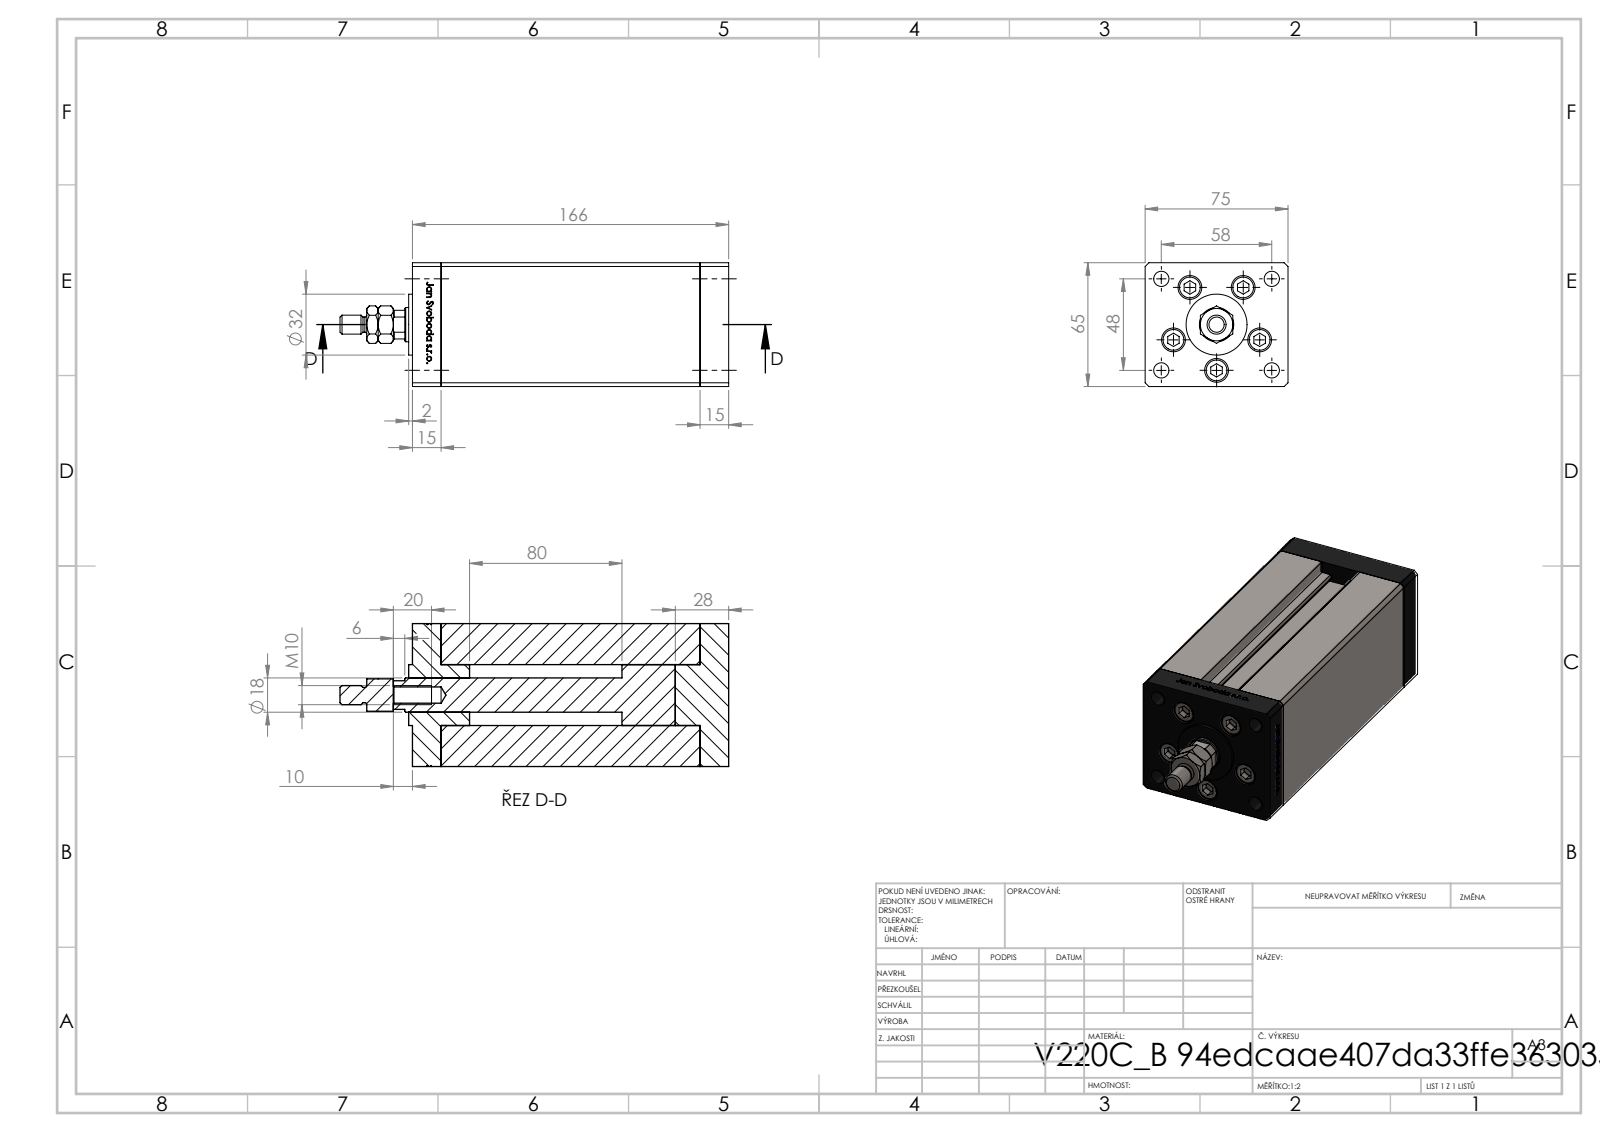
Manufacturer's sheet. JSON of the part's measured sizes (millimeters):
{"part_name": "V220C BACK_B; V220C_B MIDDLE; ALLEN BOLT; V220C_FRONT_B (+2 more)", "step_written_by": "SolidWorks 2019 (CONFIG_CONTROL_DESIGN)", "units": "millimeters", "bodies": {"solids": 15, "faces": 1232, "planar": 477, "cylindrical": 151, "other": 604}, "overall_size": [204, 75, 65], "volume_mm3": 726984, "surface_area_mm2": 129101, "round_holes": [[9, 5], [12.5, 5], [8, 4], [2, 2], [13.16, 2], [8.5, 1], [18, 1]], "round_bosses_or_shafts": [[8, 6], [32, 1], [10, 1]], "partial_cylinders_radius": [[0.93, 2], [8.5, 1]], "face_to_face_distances": [75, 65, 15, 136, 151, 166, 28, 13, 54.5, 10.5], "hole_center_spacings": [24, 37.64, 15.67, 17.22, 27.71, 28.83, 29, 32.63]}
